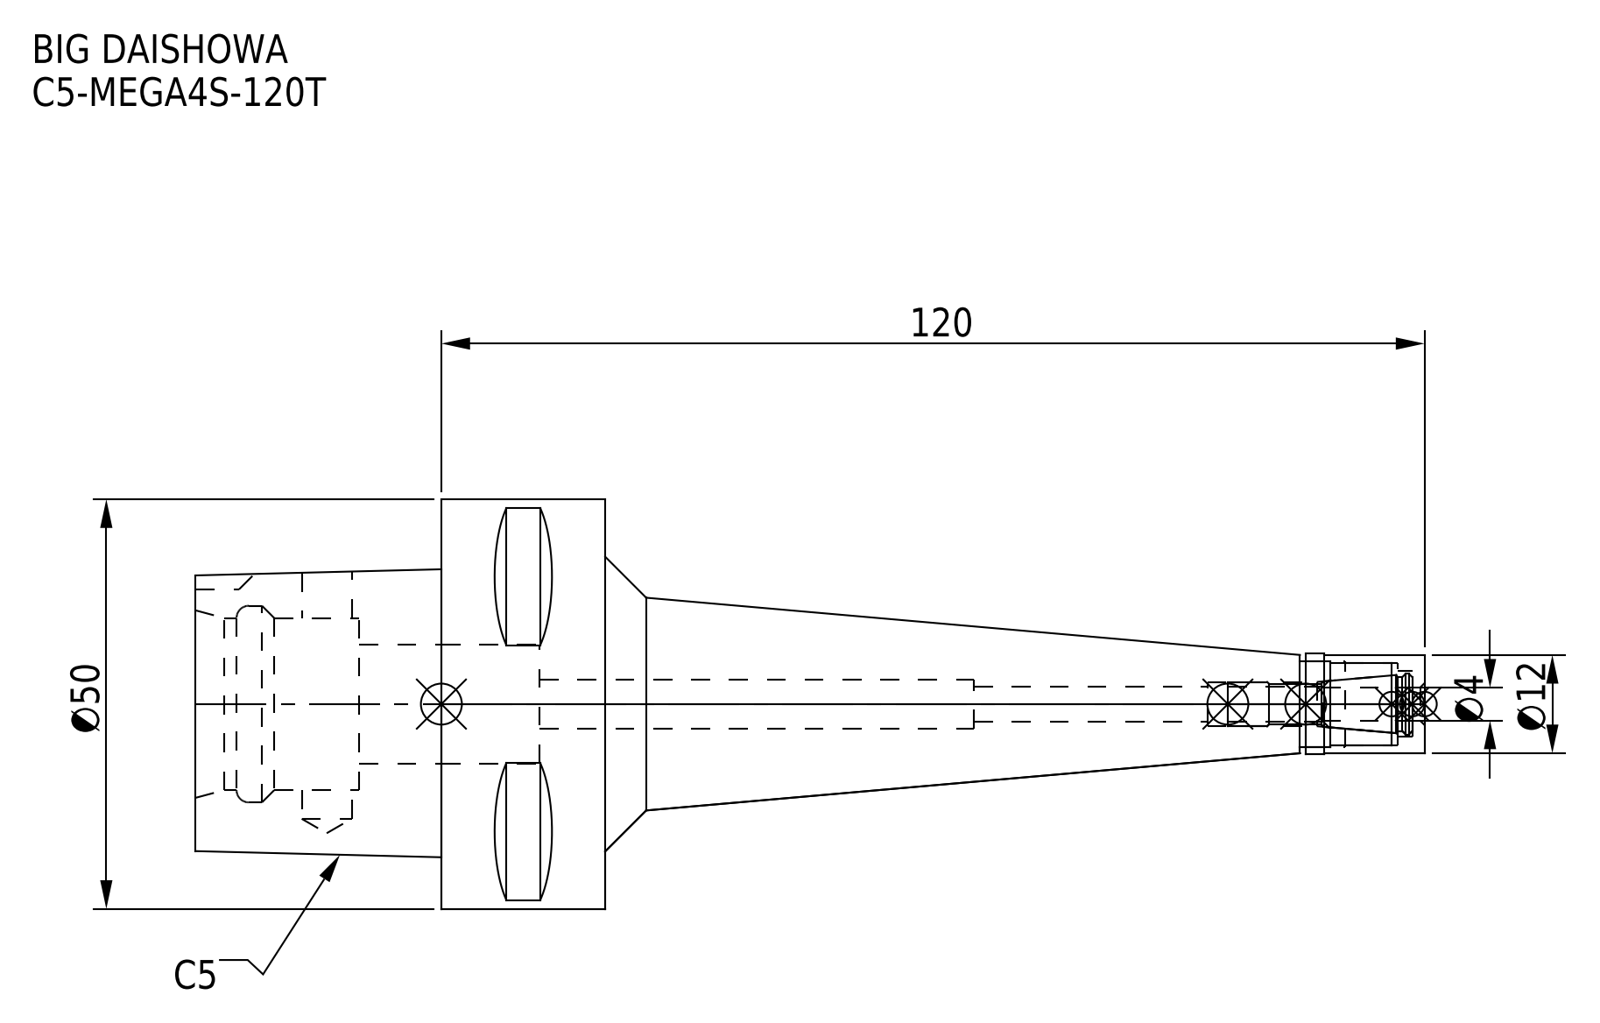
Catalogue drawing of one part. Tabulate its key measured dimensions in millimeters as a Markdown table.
| quantity | value |
| --- | --- |
| part name | C5-MEGA4S-120T_1.stp; C5-MEGA4S-120T-040.stp; MGN4S_1.stp; C5-MEGA4S-120T-040-FreeParts (+3 more) |
| STEP written by | SolidWorks 2019 (CONFIG_CONTROL_DESIGN) |
| units | millimeters |
| bodies | 2 solids, 93 faces (38 planar, 37 cylindrical, 18 other) |
| overall size | 150 × 50 × 50 |
| volume | 80 946 mm³ |
| surface area | 20 809 mm² |
| round holes (diameter × count) | 4.1 × 1, 4.2 × 1, 5.4 × 1, 6 × 1, 6.1 × 1, 8 × 1, 10 × 1, 10.5 × 1, 14.5 × 1, 21 × 1, 24 × 1 |
| round bosses / shafts (diameter × count) | 50 × 1, 12.3 × 1, 12 × 1 |
| partial cylindrical surfaces (radius × count) | 4 × 1 |
| main face-to-face distances | 20, 30, 50, 44, 10, 19.18, 12, 8, 22, 42 |
